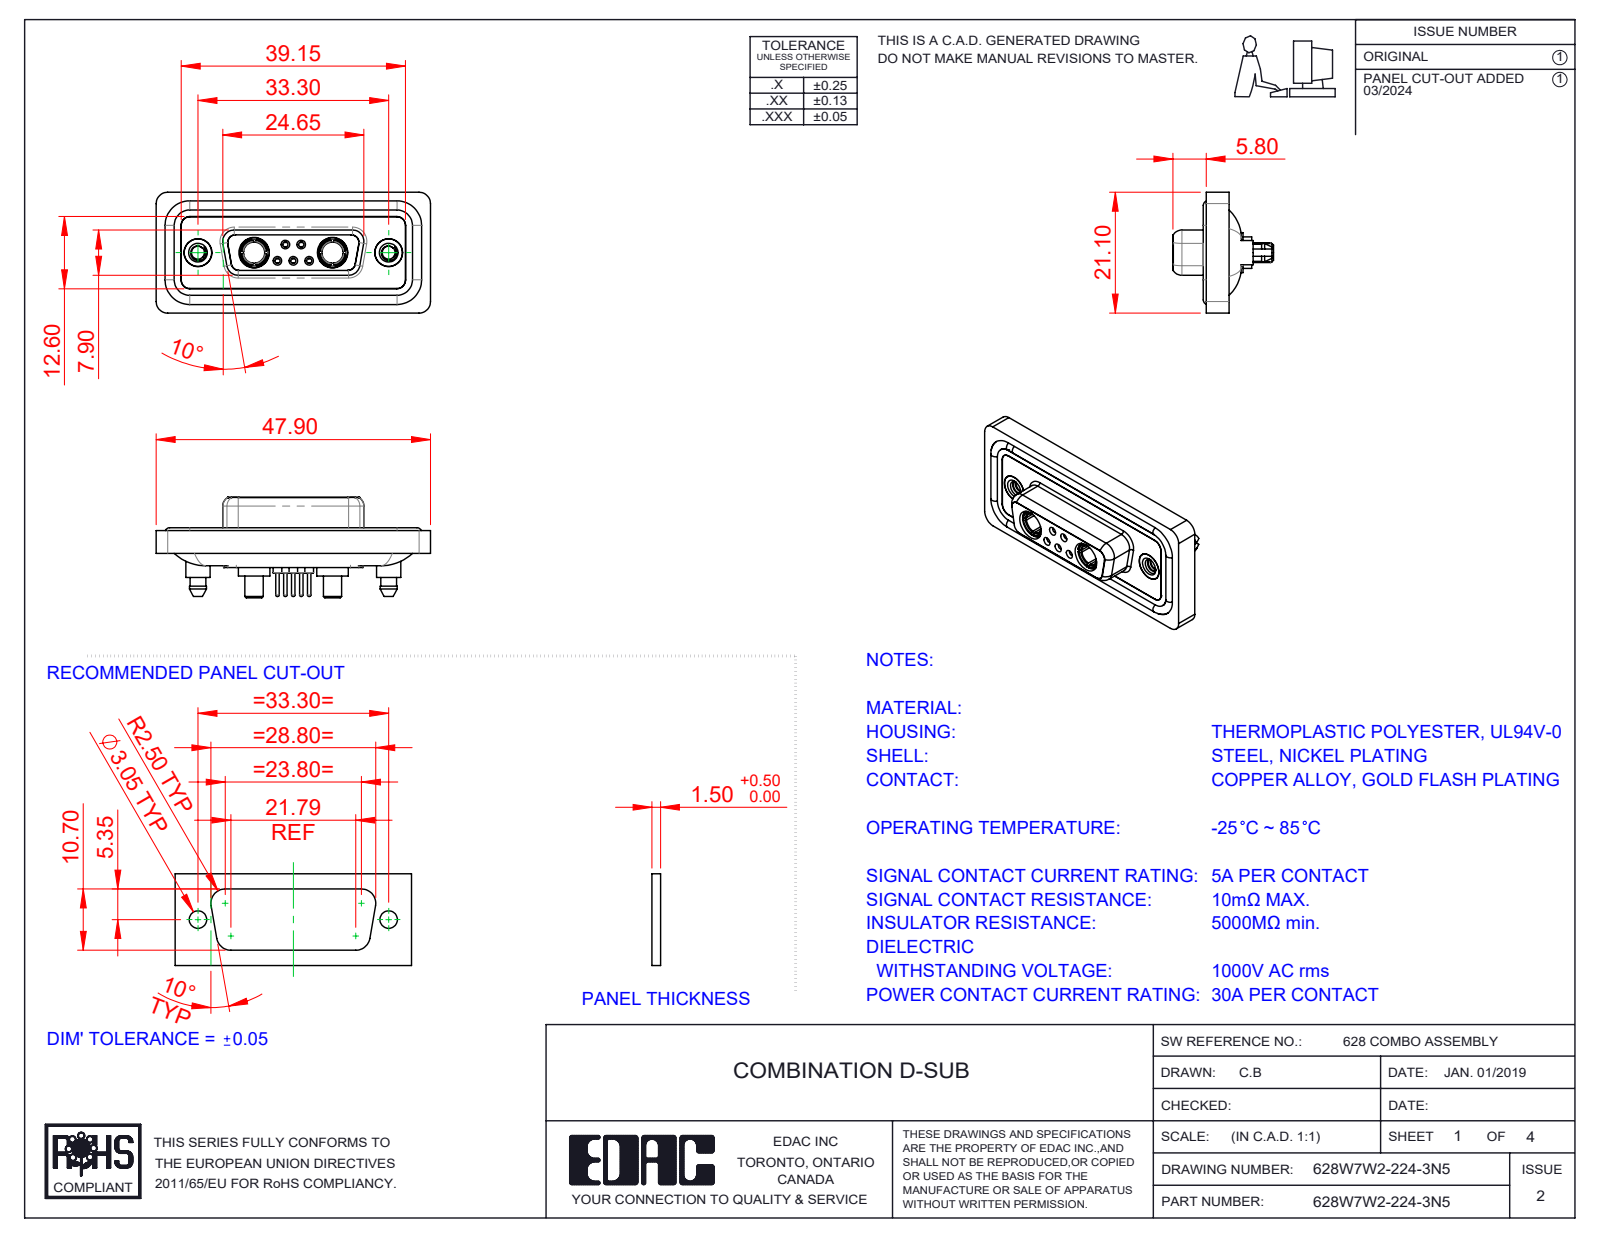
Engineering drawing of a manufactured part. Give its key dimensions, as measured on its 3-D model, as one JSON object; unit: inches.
{"part_name": "628Combo Shell Front_15 Contacts; 628Combo Housing_7W2; 628Combo Shell Rear_15 Contacts; 628W7W2-224-3N5 (+5 more)", "step_written_by": "SolidWorks 2023 (CONFIG_CONTROL_DESIGN)", "units": "inches", "bodies": {"solids": 16, "faces": 859, "planar": 254, "cylindrical": 361, "other": 244}, "overall_size": [1.886, 0.831, 0.691], "volume_in3": 0.38, "surface_area_in2": 15.85, "round_holes": [[0.035, 5], [0.043, 5], [0.059, 5], [0.079, 5], [0.191, 4], [0.063, 3], [0.067, 2], [0.089, 2], [0.146, 2], [0.157, 2], [0.159, 2], [0.197, 2]], "round_bosses_or_shafts": [[0.063, 6], [0.087, 5], [0.024, 5], [0.217, 2], [0.213, 2], [0.205, 2], [0.195, 2], [0.195, 2]], "partial_cylinders_radius": [[0.059, 24], [0.079, 20], [0.053, 12], [0.063, 10], [0.01, 4], [0.02, 4], [0.024, 4], [0.026, 4]], "face_to_face_distances": [0.016, 0.071, 0.063, 0.02, 0.114, 0.043, 0.293, 0.222, 0.26, 0.278], "hole_center_spacings": [0.124, 0.109, 0.386, 0.925, 0.17, 0.17, 0.198, 0.198]}
